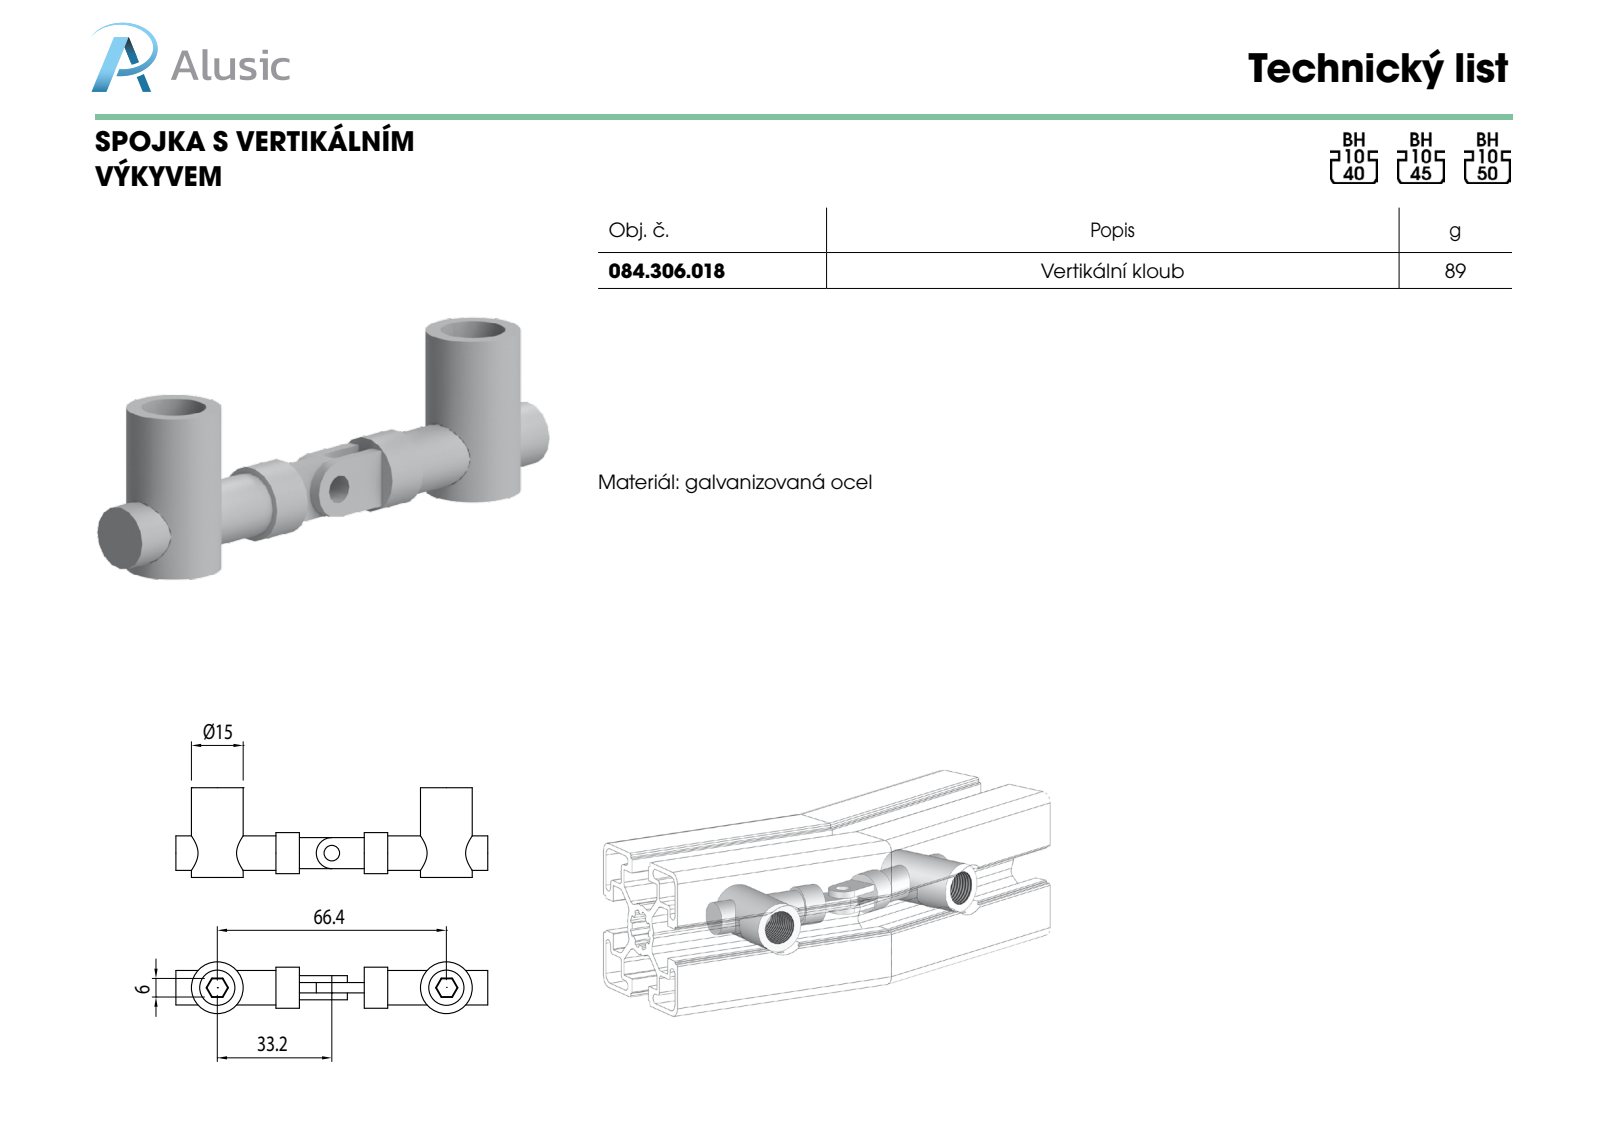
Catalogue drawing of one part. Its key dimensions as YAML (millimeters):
part_name: "1.JNT.002C; 1.JNT.002B; 084.306.018; 1.JNT.002A"
step_written_by: "SolidWorks 2012 (CONFIG_CONTROL_DESIGN)"
units: millimeters
bodies: {solids: 4, faces: 59, planar: 22, cylindrical: 31, other: 6}
overall_size: [90.4, 26, 15]
volume: 11332
surface_area: 7938
round_holes:
  - {diameter: 10.2, count: 2}
  - {diameter: 4.5, count: 1}
  - {diameter: 10, count: 1}
round_bosses_or_shafts:
  - {diameter: 15, count: 2}
  - {diameter: 11.9, count: 1}
  - {diameter: 9, count: 1}
face_to_face_distances: [2, 5, 3, 26, 35.8, 54.6, 7, 90.4, 18.8, 2.55]
hole_center_spacings: [66.4]
